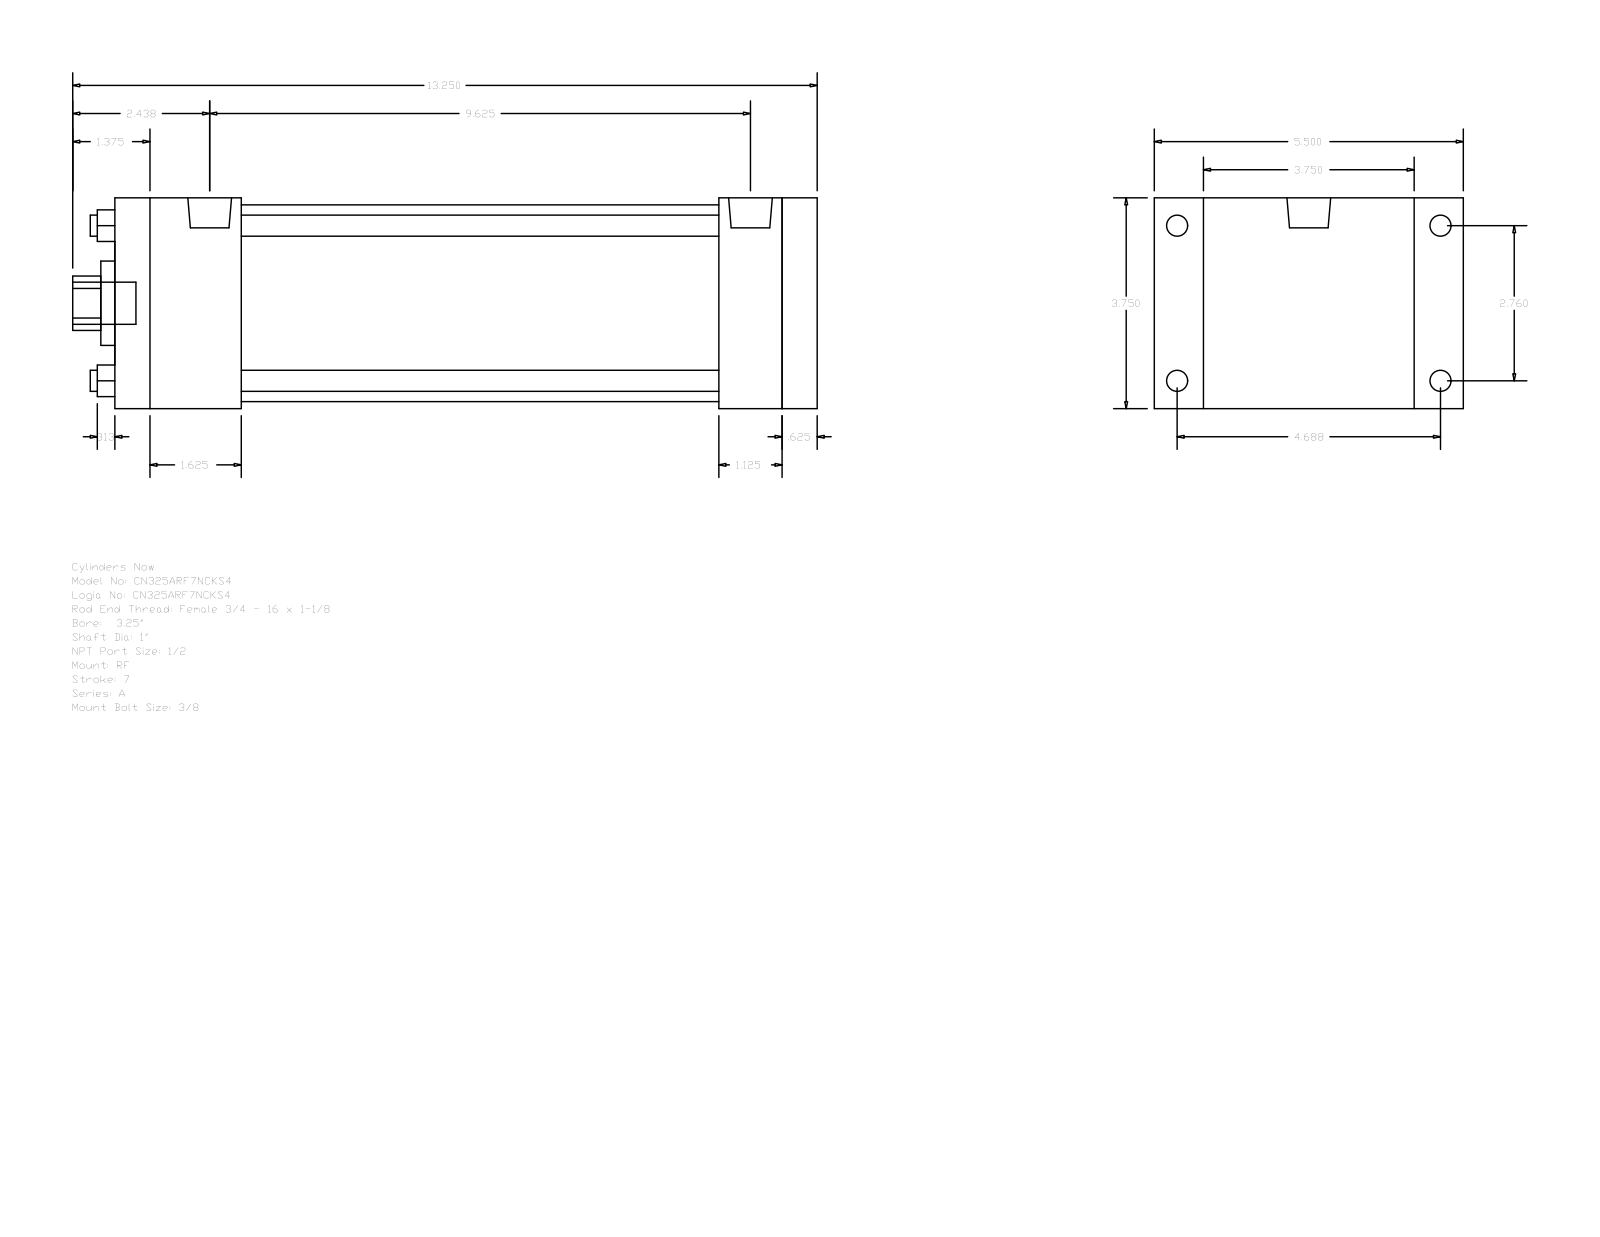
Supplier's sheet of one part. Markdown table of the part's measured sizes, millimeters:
| quantity | value |
| --- | --- |
| part name | A_RF__0325_1 |
| STEP written by | GSSL Pune (CONFIG_CONTROL_DESIGN) |
| units | millimeters |
| bodies | 0 solids, 92 faces (64 planar, 28 cylindrical, 0 other) |
| overall size | 336.55 × 139.7 × 95.25 |
| round holes (diameter × count) | 9.53 × 4, 25.4 × 1, 38.1 × 1, 88.9 × 1 |
| round bosses / shafts (diameter × count) | 9.53 × 4, 8.73 × 4, 19.77 × 2, 19.05 × 1 |
| partial cylindrical surfaces (radius × count) | 12.29 × 1 |
| main face-to-face distances | 95.24, 317.5, 15.87, 301.63, 22.23, 117.47, 273.05, 28.58, 44.45, 57.15 |
| hole center spacings | 49.57, 70.1, 99.14 |
